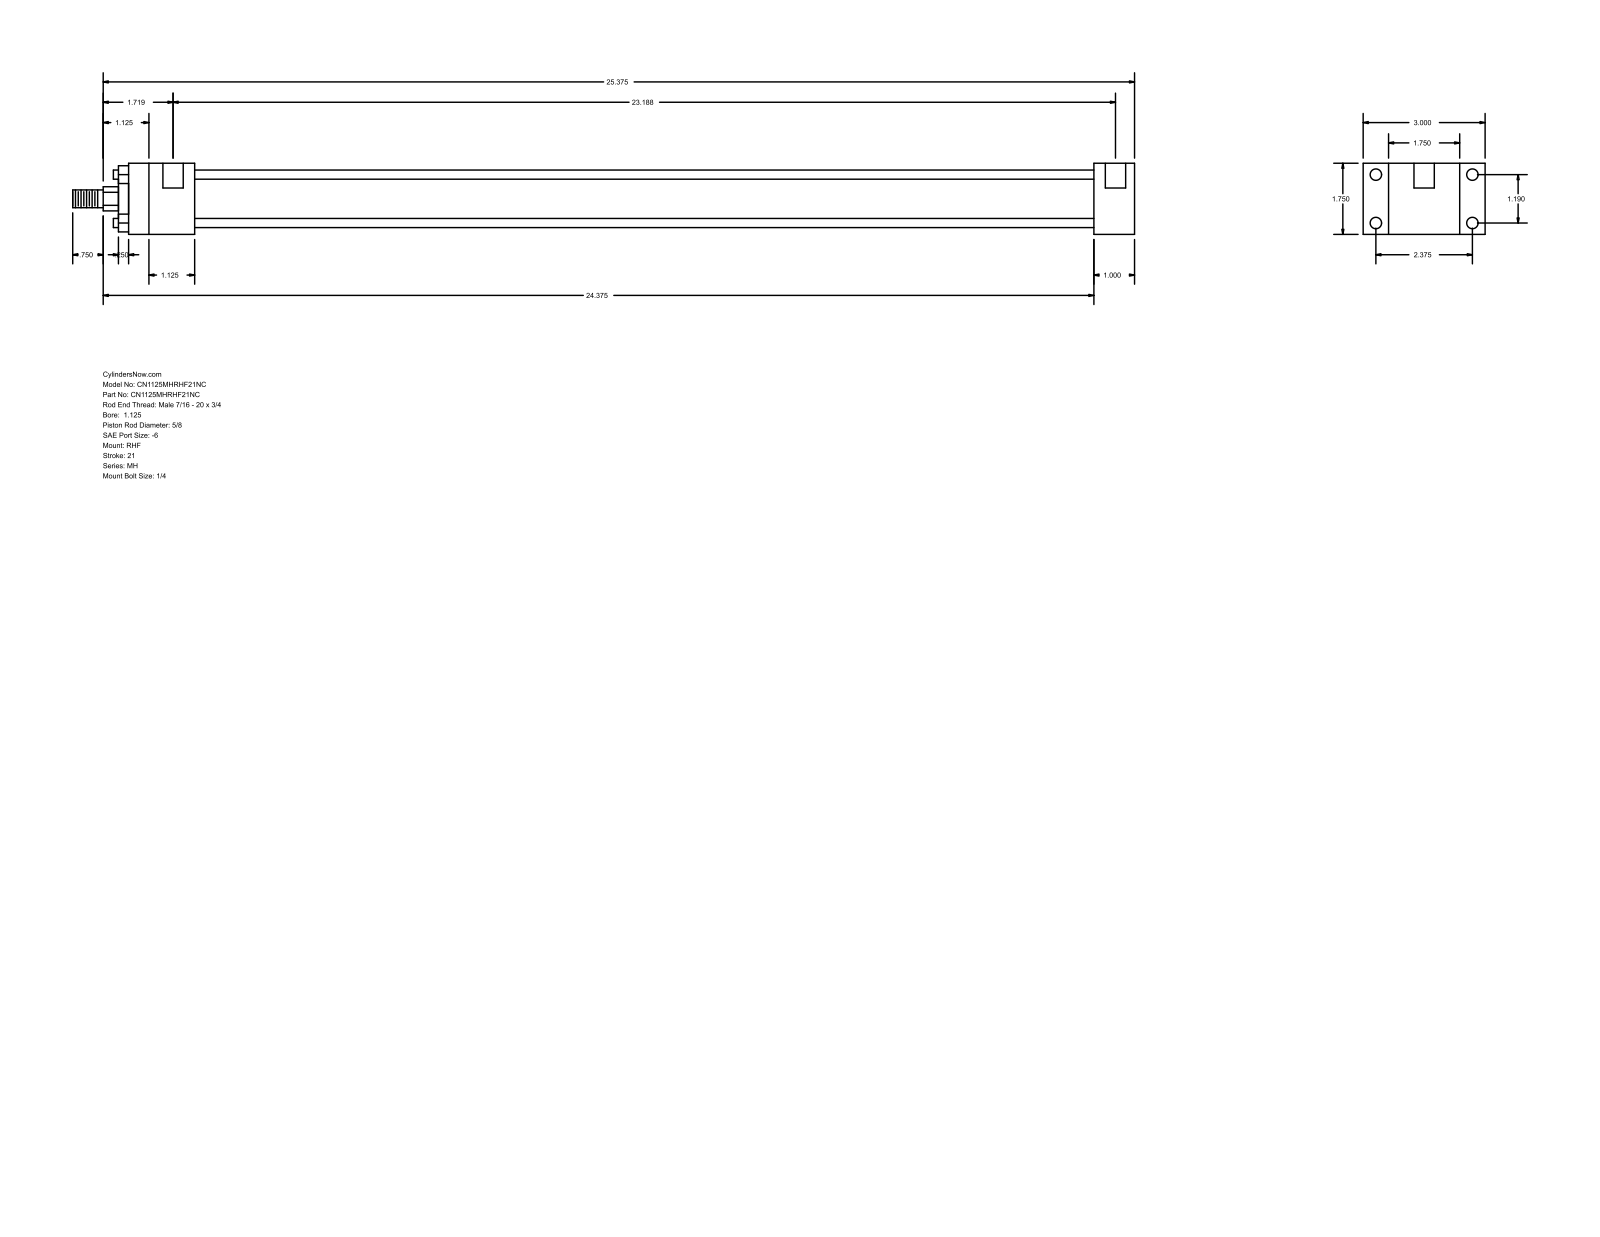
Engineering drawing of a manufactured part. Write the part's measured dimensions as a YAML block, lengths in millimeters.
part_name: "MH_RHF__0112_0.625"
step_written_by: "GSSL Pune (CONFIG_CONTROL_DESIGN)"
units: millimeters
bodies: {solids: 0, faces: 88, planar: 60, cylindrical: 28, other: 0}
overall_size: [663.58, 76.2, 44.45]
round_holes:
  - {diameter: 5.56, count: 4}
  - {diameter: 7.14, count: 4}
  - {diameter: 12.7, count: 2}
round_bosses_or_shafts:
  - {diameter: 5.71, count: 4}
  - {diameter: 34.92, count: 1}
  - {diameter: 28.57, count: 1}
  - {diameter: 15.88, count: 1}
  - {diameter: 11.11, count: 1}
partial_cylinders:
  - {radius: 7.54, count: 1}
face_to_face_distances: [44.46, 15.87, 25.4, 60.33, 76.2, 561.97, 587.37, 41.27, 603.24, 628.64]
hole_center_spacings: [30.22, 60.32, 67.47, 585.79, 3.17, 588.96]
